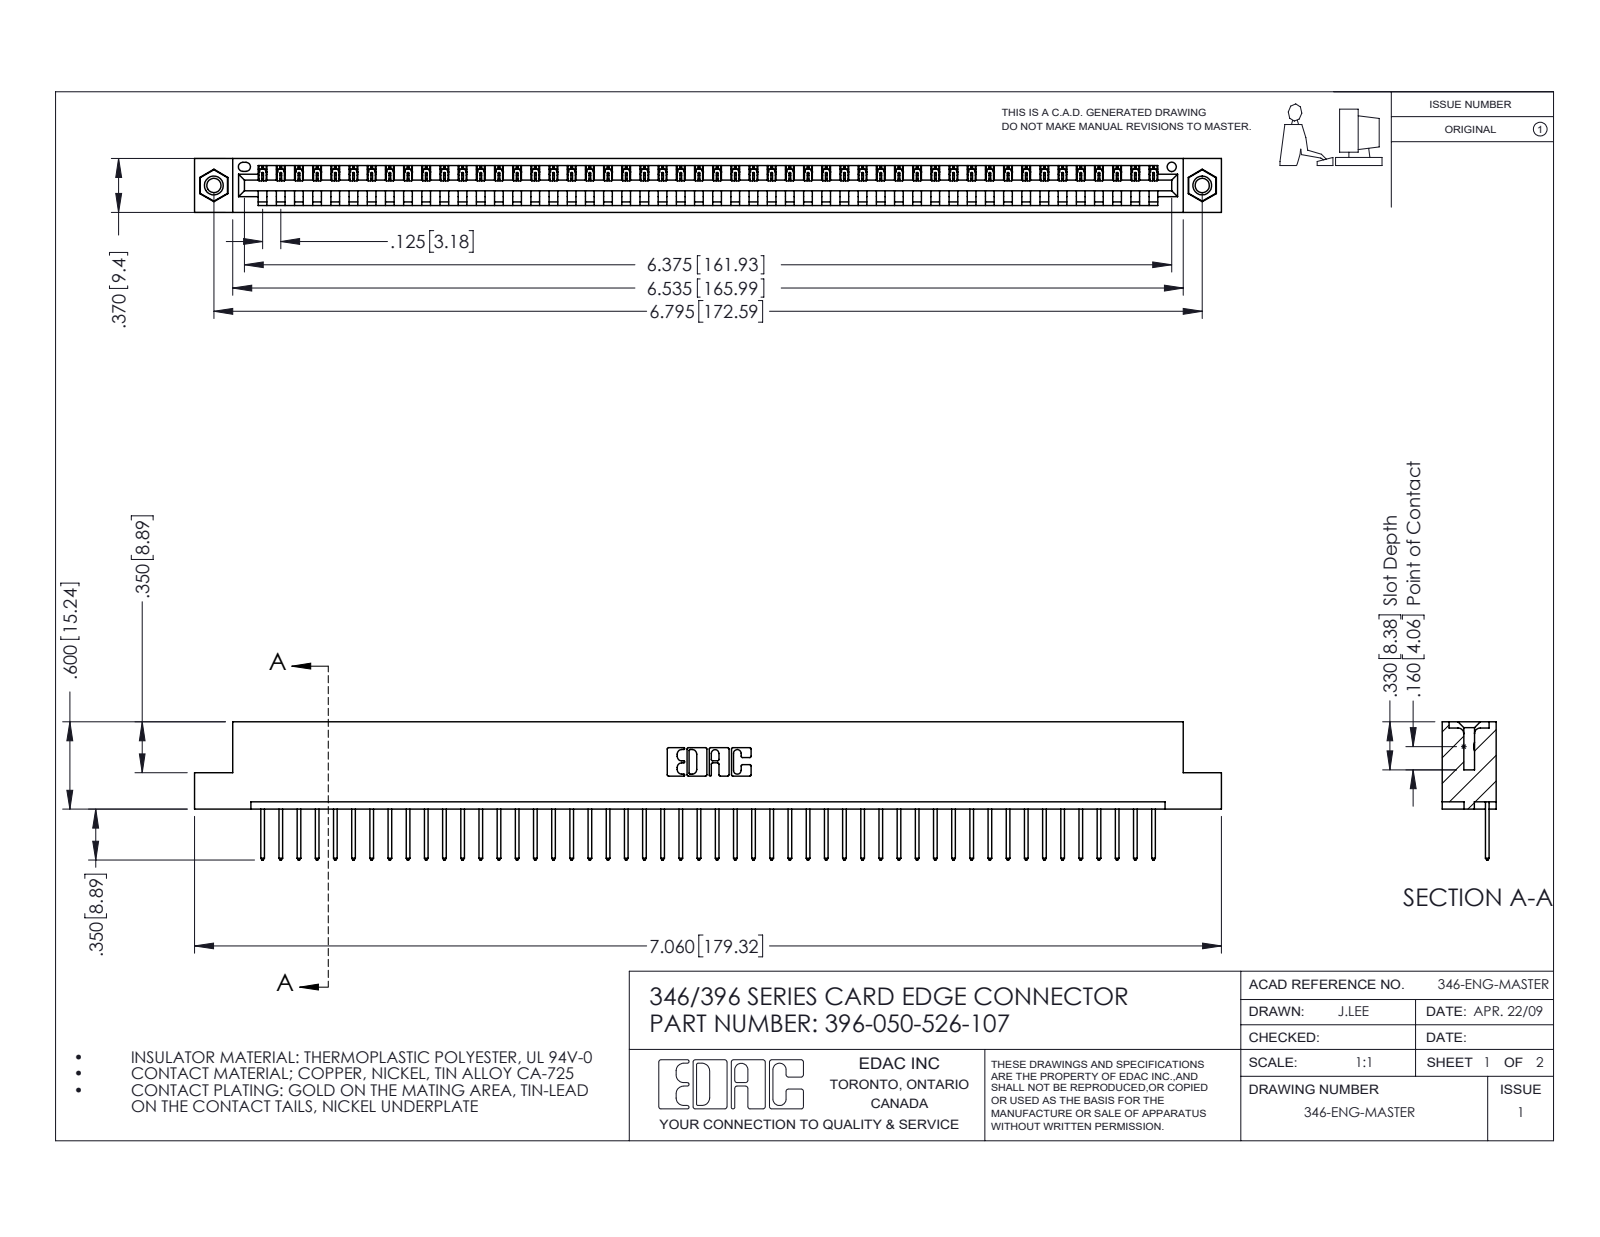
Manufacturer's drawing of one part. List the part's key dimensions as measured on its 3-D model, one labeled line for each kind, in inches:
Part name (STEP PRODUCT): 345-250-001_345-250-005-103; 396-050-526-107; 345-292-001_345-293-126; 346 Part_Flush Mounting Lugs - 0.156 Dia-TI
STEP written by: SolidWorks 2016 (CONFIG_CONTROL_DESIGN)
Units: inches
Bodies: 53 solids, 3082 faces (2108 planar, 958 cylindrical, 16 other)
Overall size (bounding box): 7.06 × 0.95 × 0.37
Volume: 1.048 in³ · Surface area: 33.37 in²
Round holes (diameter × count): ⌀0.098 ×2, ⌀0.125 ×2, ⌀0.156 ×2, ⌀0.064 ×1
Round bosses / shafts (diameter × count): ⌀0.155 ×2
Partial cylindrical surfaces — rounded edges, fillets, slot ends (radius × count): R0.006 ×100, R0.01 ×100, R0.01 ×22, R0.007 ×6, R0.031 ×6, R0.026 ×3, R0.031 ×2, R0.04 ×2
Main face-to-face distances: 0.048, 0.322, 0.37, 0.25, 0.072, 0.298, 0.025, 0.148, 0.222, 0.1
Hole centre spacings: 0.246, 6.586, 6.795
